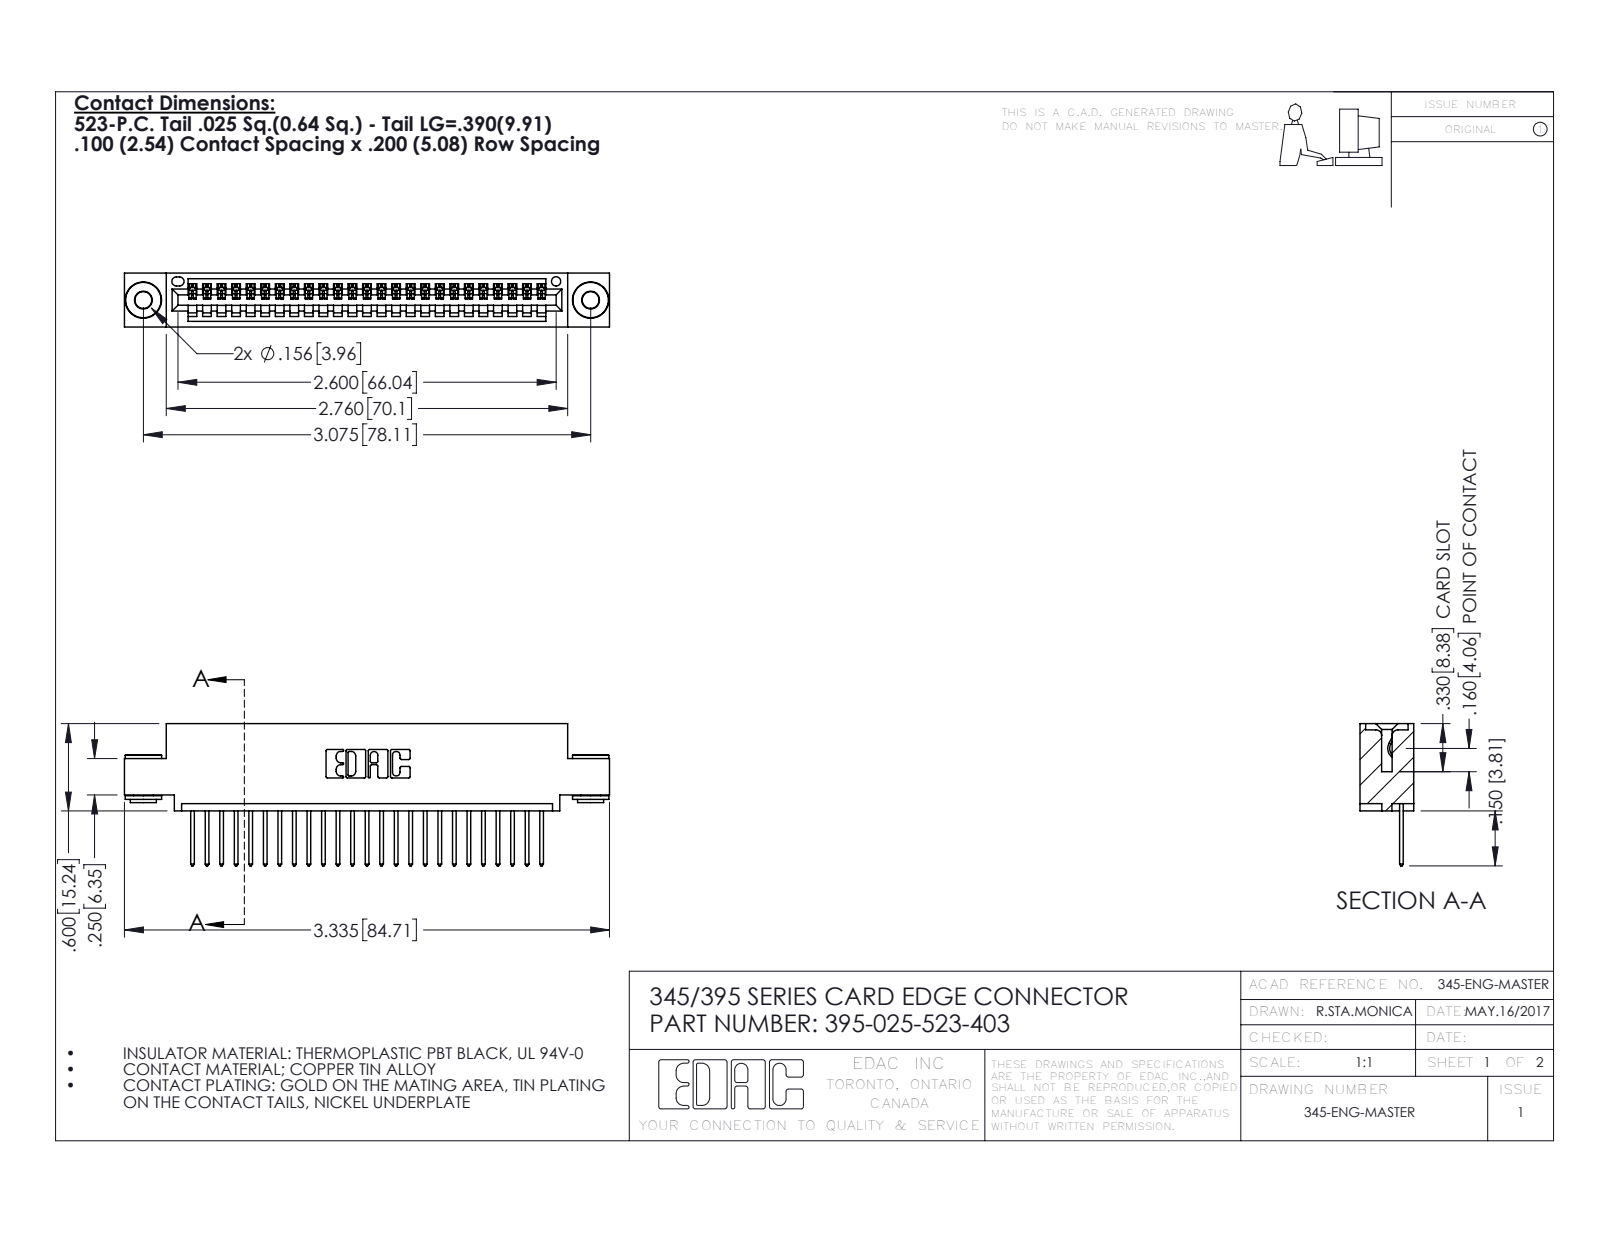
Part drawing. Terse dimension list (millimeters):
name: 345-292-001_345-293-123; 395-025-523-403; 345-250-002_345-250-002-102; 345 Part_0.110 Offset - 0.156 Dia-TH
written by: SolidWorks 2016 (CONFIG_CONTROL_DESIGN)
unit: mm
bodies: 28 solids, 1618 faces (1094 planar, 516 cylindrical, 8 other)
size: 84.7 × 24.8 × 9.4
volume: 7 850 mm³; area: 10 520 mm²
holes: 2× ⌀2.9, 2× ⌀4, 1× ⌀1.6
bosses: 2× ⌀6.4, 2× ⌀4.6, 2× ⌀3.5
rounds: 50× R0.2, 50× R0.3, 22× R0.3, 6× R0.2, 6× R0.8, 3× R0.7, 2× R0.8, 2× R1
face distances: 1.8, 7.6, 9.4, 5.1, 0.6, 2.5, 6.9, 5.7, 3.8, 1.8
hole spacings: 6.9, 72.1, 78.1
